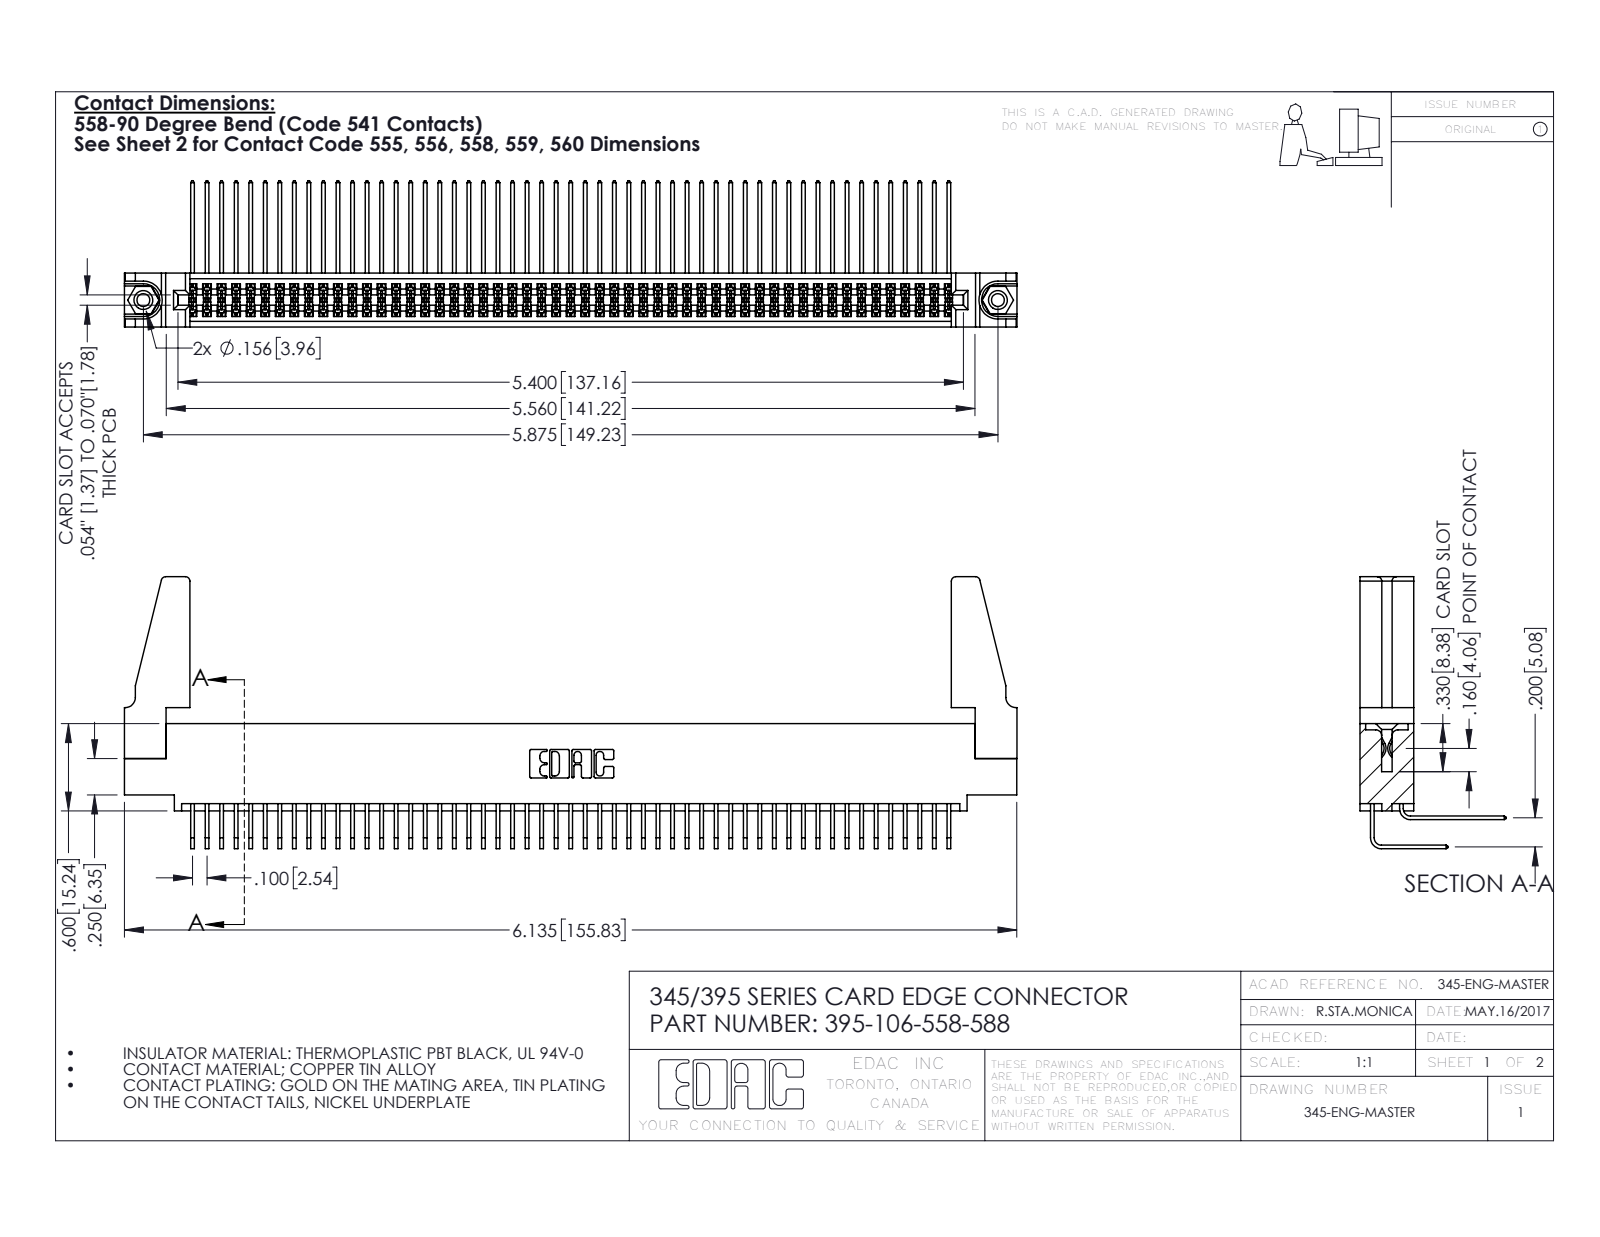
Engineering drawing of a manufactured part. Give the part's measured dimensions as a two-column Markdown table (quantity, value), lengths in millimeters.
| quantity | value |
| --- | --- |
| part name | 345-250-001_345-250-001-102; 345-220-078_345-220-088; 345-292-001_558 Tail - 2; 345-292-001_558 559 Tail - 1 (+2 more) |
| STEP written by | SolidWorks 2016 (CONFIG_CONTROL_DESIGN) |
| units | millimeters |
| bodies | 111 solids, 5766 faces (3866 planar, 1884 cylindrical, 16 other) |
| overall size | 155.9 × 47.5 × 25.5 |
| volume | 19 030 mm³ |
| surface area | 29 630 mm² |
| round holes (diameter × count) | 2.3 × 2, 3.2 × 2, 4 × 2, 1.6 × 1 |
| round bosses / shafts (diameter × count) | 3.9 × 2 |
| partial cylindrical surfaces (radius × count) | 0.2 × 160, 0.3 × 22, 0.8 × 8, 0.2 × 6, 0.8 × 6, 0.7 × 3, 0.4 × 2, 0.5 × 2 |
| main face-to-face distances | 1.8, 7.6, 5.1, 9.4, 2.5, 6.9, 0.6, 5.7, 0.6, 4.4 |
| hole center spacings | 6.9, 143.2, 149.2 |
